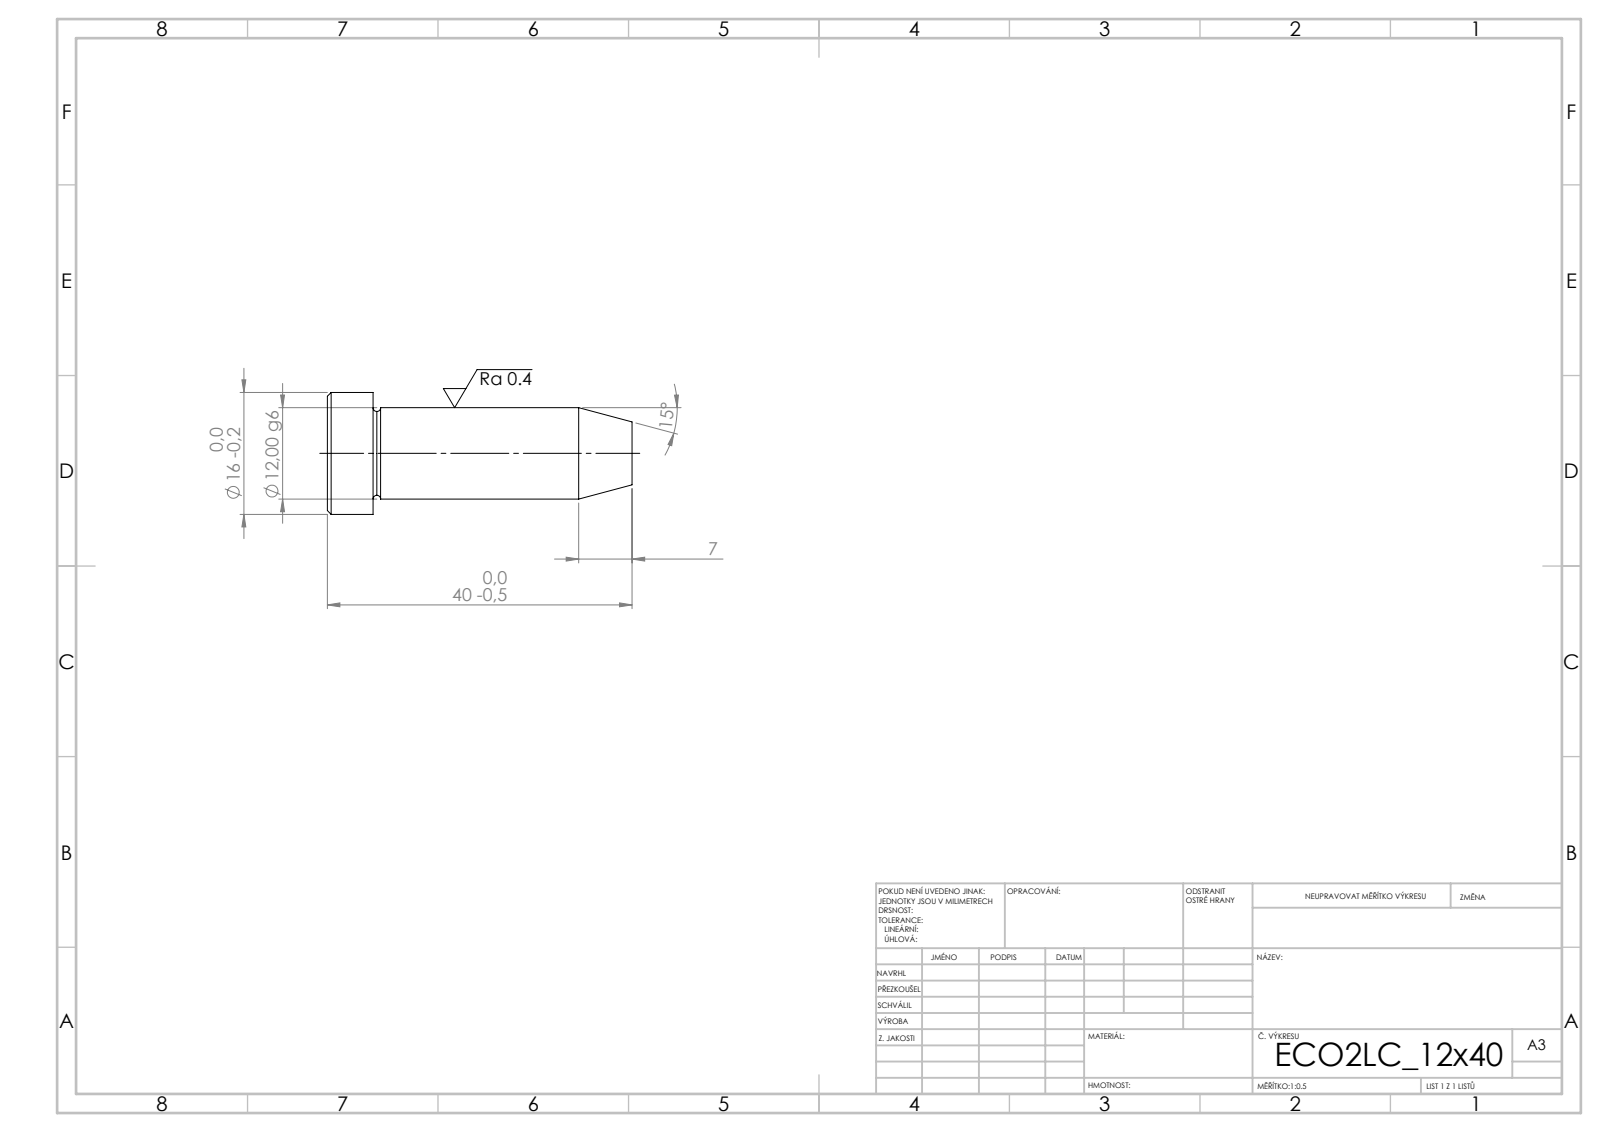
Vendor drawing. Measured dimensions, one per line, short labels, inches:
written by: SolidWorks 2019 (CONFIG_CONTROL_DESIGN)
unit: in
bodies: 1 solid, 15 faces (3 planar, 4 cylindrical, 8 other)
size: 1.575 × 0.63 × 0.63
volume: 0.294 in³; area: 2.939 in²
bosses: 1× ⌀0.63, 1× ⌀0.472
face distances: 0.236, 1.339, 1.575
